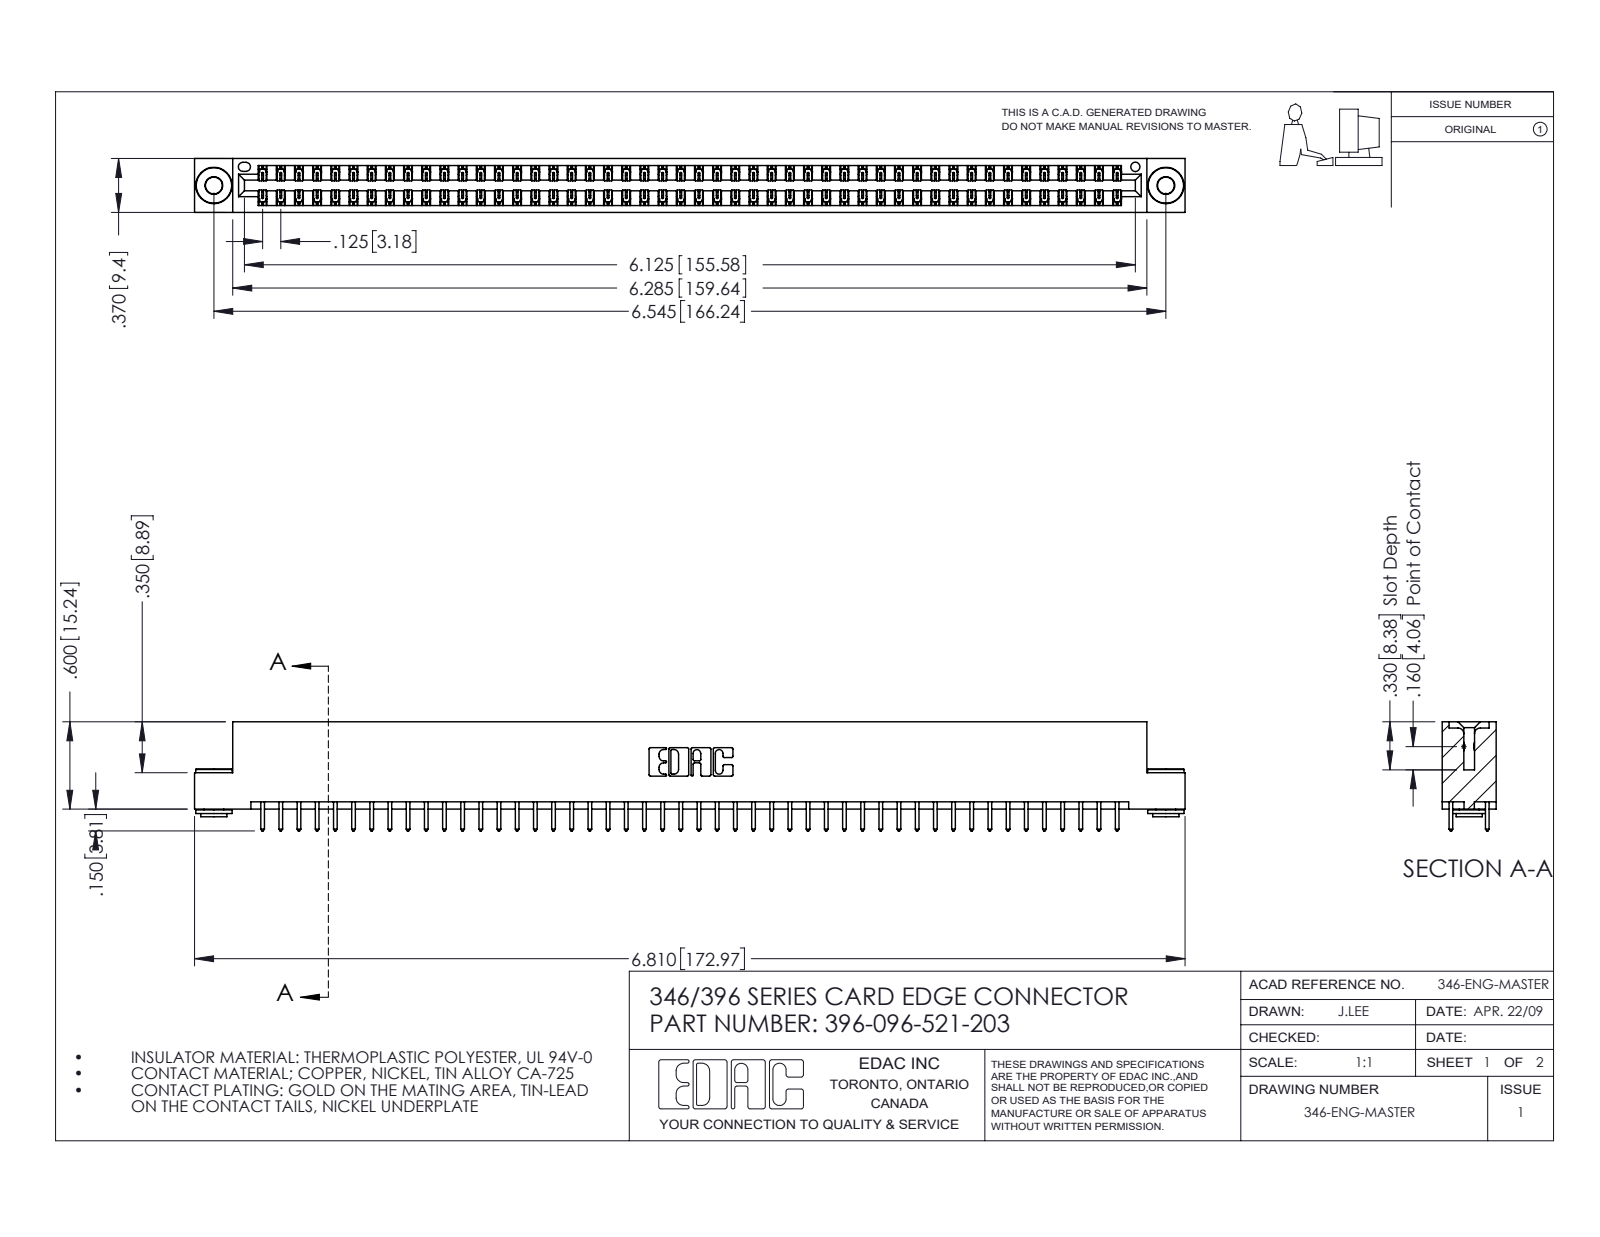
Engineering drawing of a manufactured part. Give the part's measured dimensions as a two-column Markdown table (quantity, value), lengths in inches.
| quantity | value |
| --- | --- |
| part name | 345-292-001_345-293-121; 346 Part_Flush Mounting Lugs - 0.156 Dia-TH; 396-096-521-203; 345-250-002_345-250-002-102 |
| STEP written by | SolidWorks 2016 (CONFIG_CONTROL_DESIGN) |
| units | inches |
| bodies | 99 solids, 5152 faces (3446 planar, 1698 cylindrical, 8 other) |
| overall size | 6.81 × 0.75 × 0.37 |
| volume | 1.031 in³ |
| surface area | 36.06 in² |
| round holes (diameter × count) | 0.116 × 2, 0.156 × 2, 0.064 × 1 |
| round bosses / shafts (diameter × count) | 0.25 × 2, 0.18 × 2, 0.136 × 2 |
| partial cylindrical surfaces (radius × count) | 0.006 × 144, 0.01 × 96, 0.01 × 22, 0.007 × 6, 0.031 × 6, 0.026 × 3, 0.014 × 2, 0.022 × 2 |
| main face-to-face distances | 0.048, 0.322, 0.25, 0.37, 0.025, 0.072, 0.298, 0.275, 0.148, 0.222 |
| hole center spacings | 0.246, 6.336, 6.545 |
